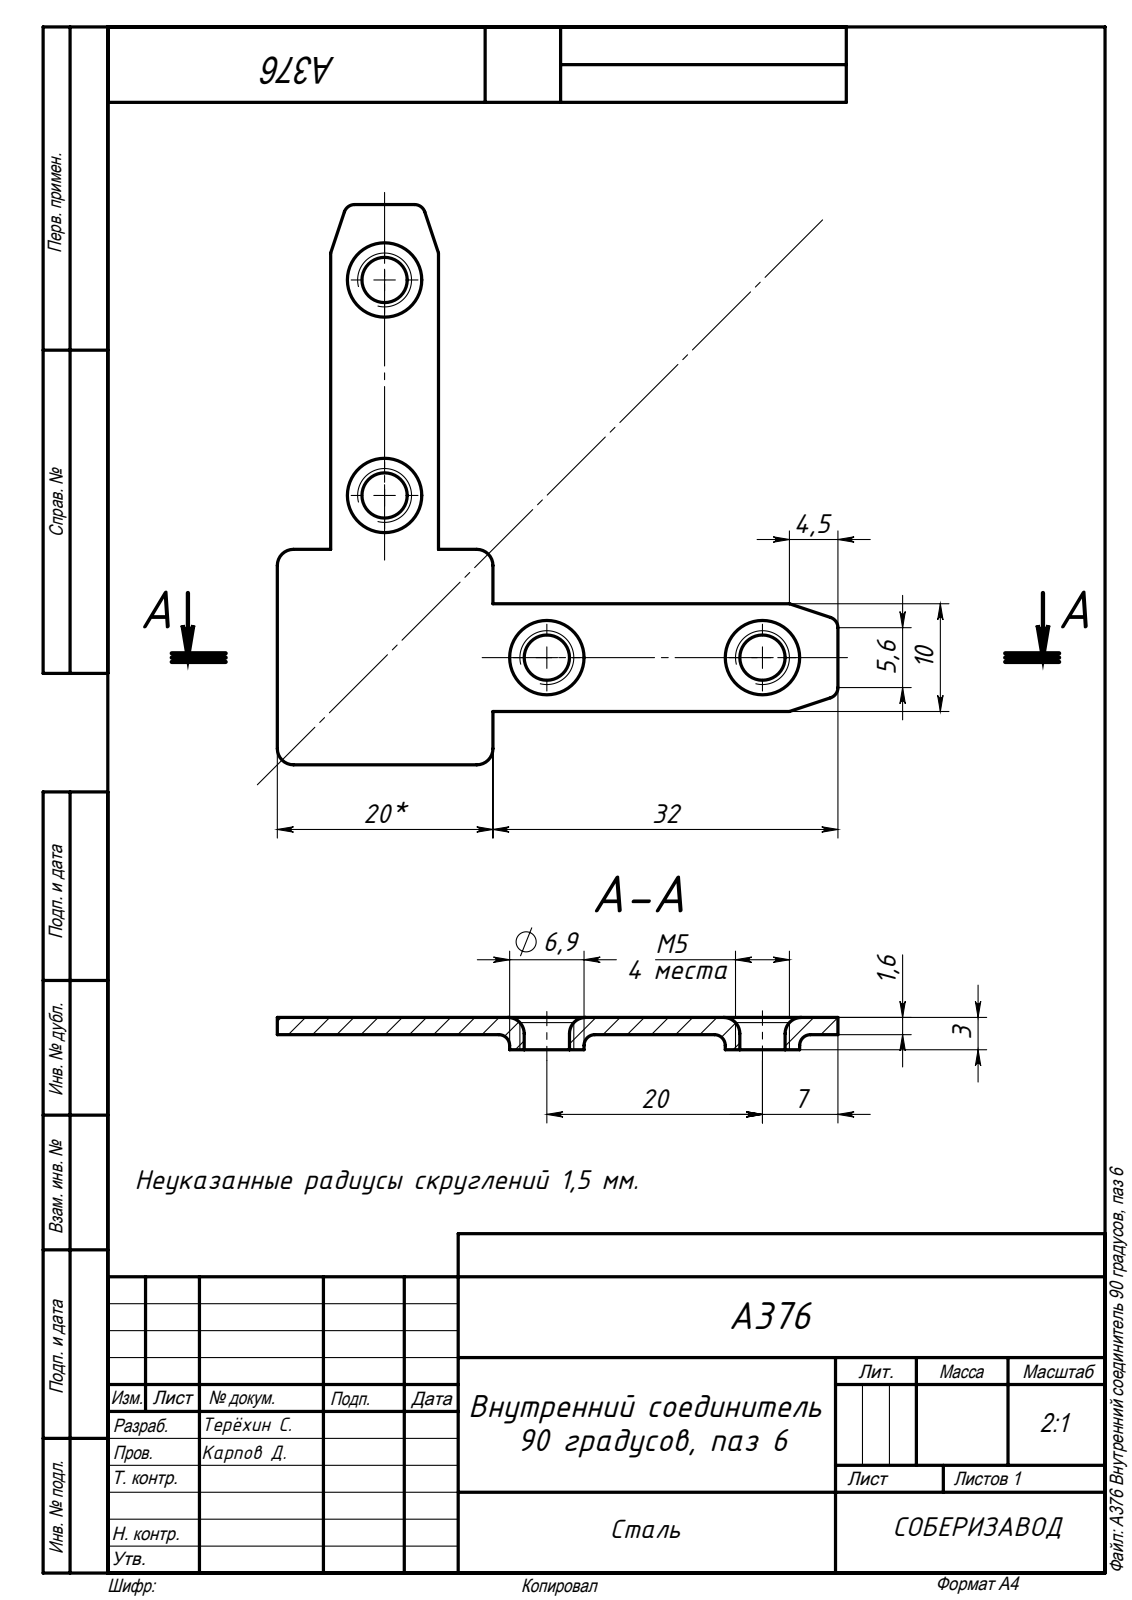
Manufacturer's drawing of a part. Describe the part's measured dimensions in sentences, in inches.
The part is named "A376 Внутренний соединитель 90 градусов, паз 6". Its 3-D file was written by "SolidWorks 2020 (AUTOMOTIVE_DESIGN)". It is 1 solid with 62 faces: 22 planar, 24 cylindrical and 16 other. Overall it measures 2.047 by 2.047 by 0.118 inches. Its volume is 0.102 cubic inches and its surface area 3.83 square inches. Round holes: 4 of diameter 0.165. Round bosses or shafts: 4 of diameter 0.272. Partial cylindrical surfaces (rounded edges, fillets, slot ends): 4 of radius 0.039, 4 of radius 0.059. The main face-to-face distances are 0.063, 0.055, 0.118, 0.394, 0.195, 0.589, 0.787, 0.593, 0.199, 2.047. The hole center spacings are 0.787, 1.502, 0.838, 1.952.
